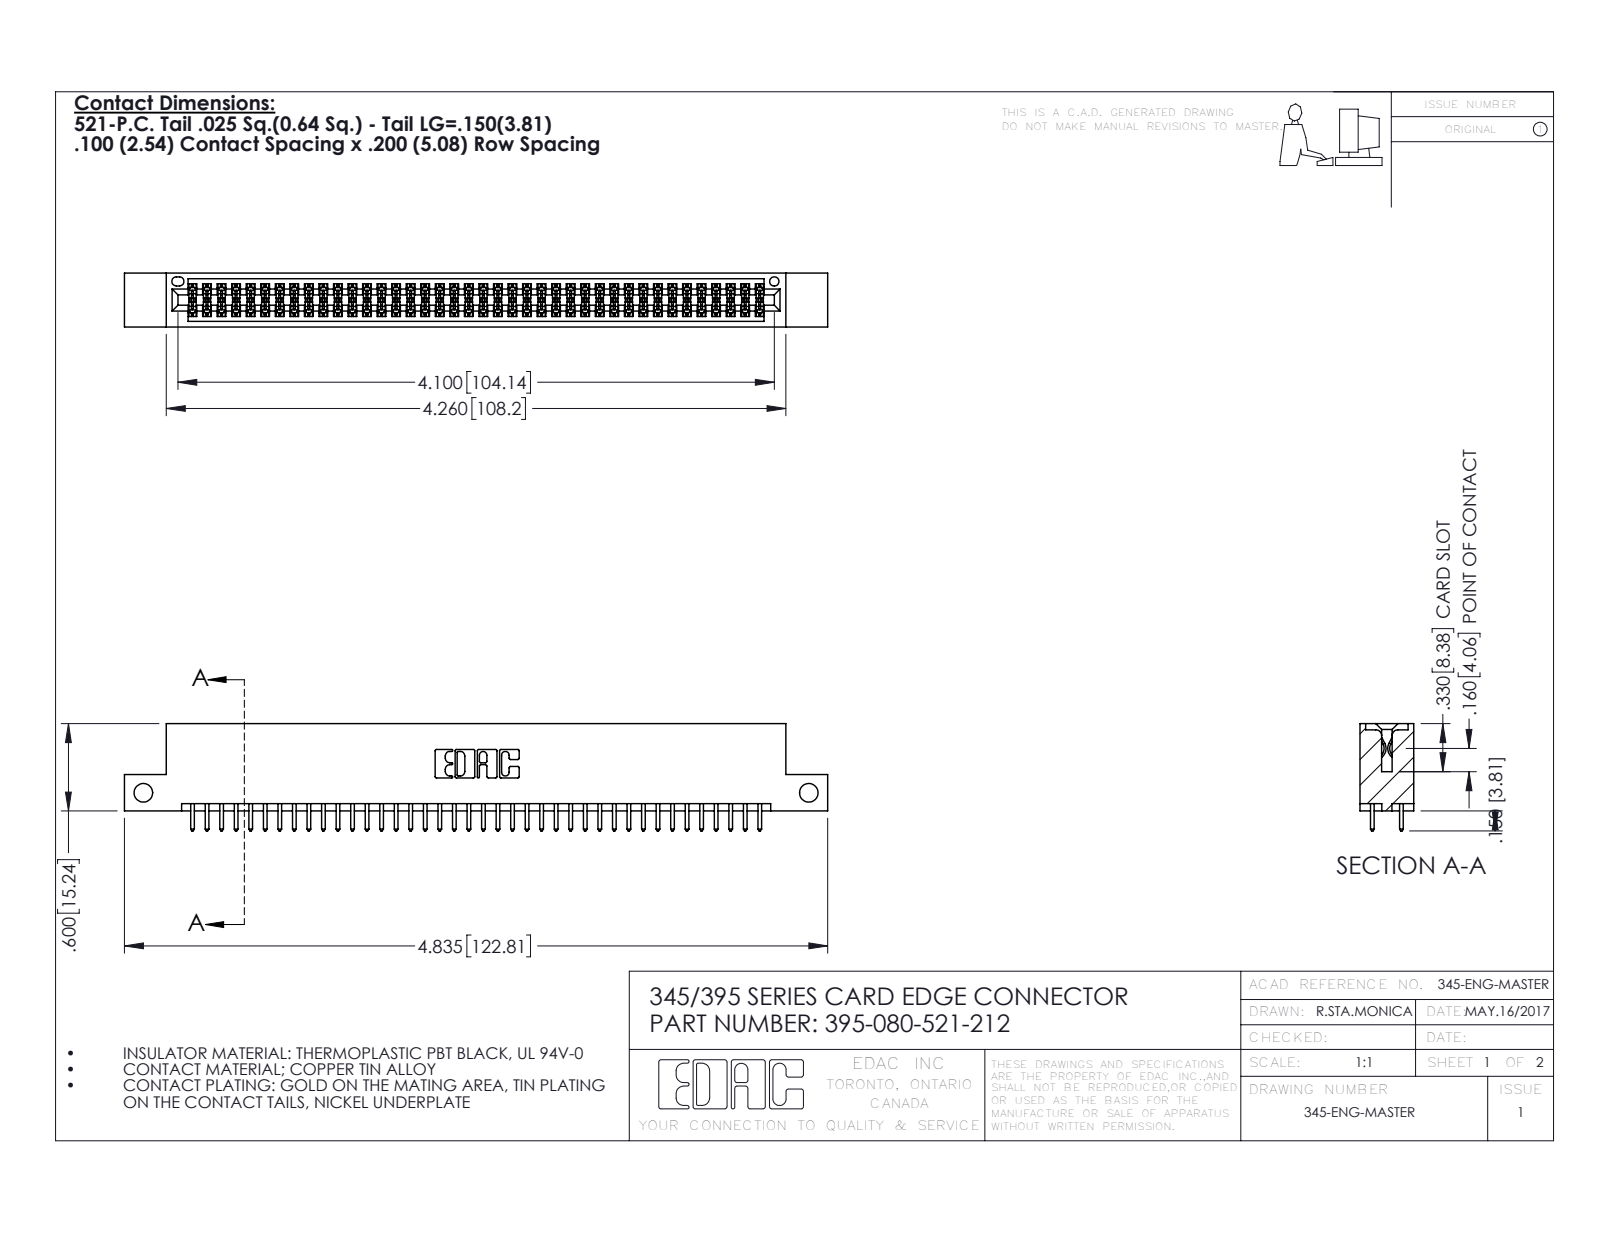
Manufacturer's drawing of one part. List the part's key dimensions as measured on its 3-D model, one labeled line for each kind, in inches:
Part name (STEP PRODUCT): 395-080-521-212; 345 Part_Flush Mounting Lugs - Side Mount; 345-292-001_345-293-121
STEP written by: SolidWorks 2016 (CONFIG_CONTROL_DESIGN)
Units: inches
Bodies: 81 solids, 4126 faces (2720 planar, 1406 cylindrical, 0 other)
Overall size (bounding box): 4.835 × 0.737 × 0.37
Volume: 0.72 in³ · Surface area: 26.42 in²
Round holes (diameter × count): ⌀0.128 ×2, ⌀0.064 ×1
Partial cylindrical surfaces — rounded edges, fillets, slot ends (radius × count): R0.006 ×120, R0.01 ×80, R0.01 ×22, R0.007 ×6, R0.031 ×6, R0.026 ×3, R0.014 ×2, R0.019 ×2
Main face-to-face distances: 0.298, 0.072, 0.2, 0.37, 0.098, 0.272, 0.025, 0.225, 0.175, 0.149
Hole centre spacings: 4.575
